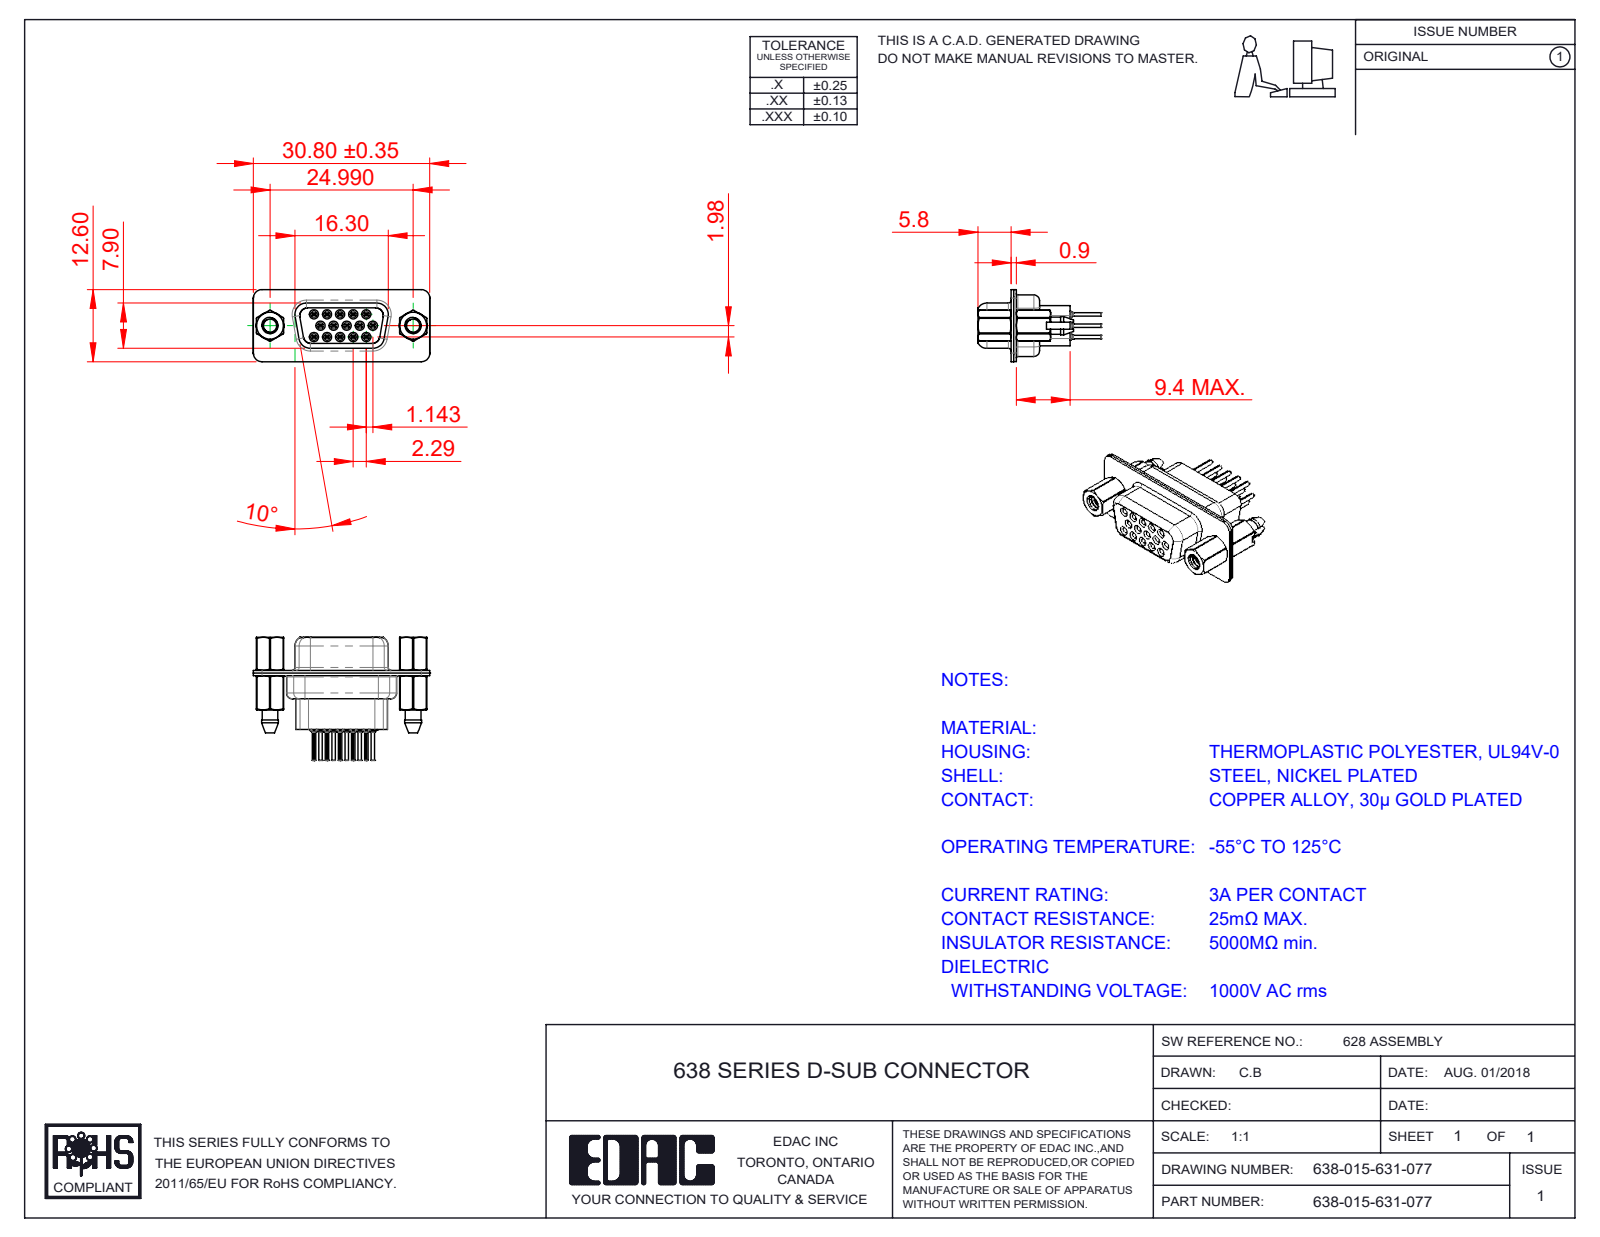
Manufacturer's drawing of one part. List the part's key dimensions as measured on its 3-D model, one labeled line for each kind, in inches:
Part name (STEP PRODUCT): 638 Contact Row 3_31; 638-015-631-077; 638 4-40 Hex Standoff; 638 Shell Rear_15 Contacts (+5 more)
STEP written by: SolidWorks 2020 (CONFIG_CONTROL_DESIGN)
Units: inches
Bodies: 22 solids, 2324 faces (586 planar, 736 cylindrical, 1002 other)
Overall size (bounding box): 1.213 × 0.846 × 0.496
Volume: 0.135 in³ · Surface area: 11.31 in²
Round holes (diameter × count): ⌀0.008 ×15, ⌀0.031 ×15, ⌀0.039 ×15, ⌀0.043 ×15, ⌀0.063 ×15, ⌀0.067 ×15, ⌀0.071 ×15, ⌀0.079 ×2, ⌀0.089 ×2, ⌀0.09 ×2, ⌀0.157 ×2, ⌀0.159 ×2
Round bosses / shafts (diameter × count): ⌀0.079 ×15, ⌀0.059 ×15, ⌀0.047 ×15, ⌀0.024 ×15, ⌀0.195 ×2, ⌀0.189 ×2, ⌀0.11 ×2
Partial cylindrical surfaces — rounded edges, fillets, slot ends (radius × count): R0.004 ×30, R0.059 ×22, R0.079 ×12, R0.011 ×10, R0.061 ×8, R0.053 ×5, R0.01 ×4, R0.02 ×4
Main face-to-face distances: 0.018, 0.035, 0.016, 0.056, 0.26, 0.35, 0.187, 0.276, 0.228, 0.09
Hole centre spacings: 0.156, 0.09, 0.18, 0.09, 0.238, 0.238, 0.27, 0.312
